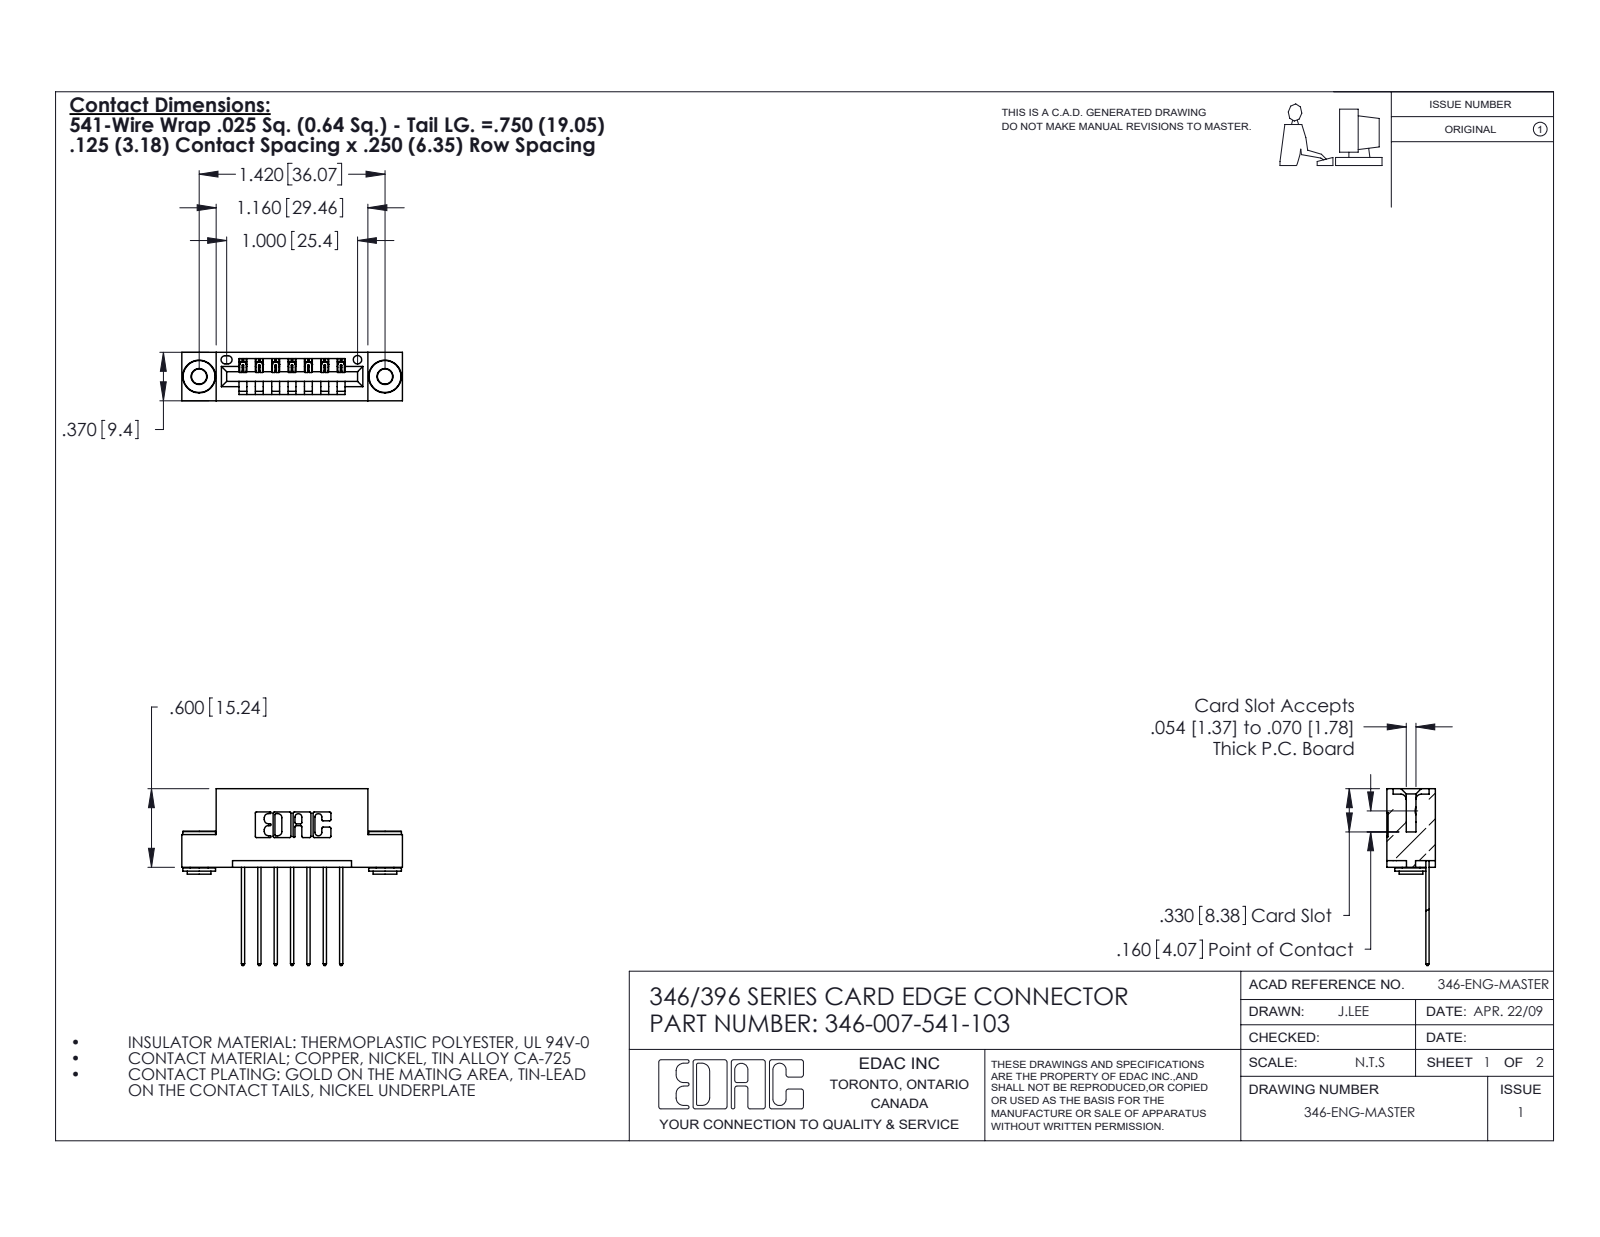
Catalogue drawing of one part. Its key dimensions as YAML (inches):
part_name: "345-292-001_345-293-141; 345-250-002_345-250-002-102; 346-007-541-103; 346 Part_Flush Mounting Lugs - 0.156 Dia-TH"
step_written_by: "SolidWorks 2020 (CONFIG_CONTROL_DESIGN)"
units: inches
bodies: {solids: 10, faces: 580, planar: 380, cylindrical: 192, other: 8}
overall_size: [1.685, 1.35, 0.37]
volume: 0.237
surface_area: 7.535
round_holes:
  - {diameter: 0.116, count: 2}
  - {diameter: 0.156, count: 2}
  - {diameter: 0.064, count: 1}
round_bosses_or_shafts:
  - {diameter: 0.25, count: 2}
  - {diameter: 0.18, count: 2}
  - {diameter: 0.136, count: 2}
partial_cylinders:
  - {radius: 0.01, count: 22}
  - {radius: 0.006, count: 14}
  - {radius: 0.01, count: 14}
  - {radius: 0.007, count: 6}
  - {radius: 0.031, count: 6}
  - {radius: 0.026, count: 3}
  - {radius: 0.031, count: 2}
  - {radius: 0.04, count: 2}
face_to_face_distances: [0.25, 0.048, 0.322, 0.37, 0.025, 0.072, 0.298, 0.148, 0.222, 0.1]
hole_center_spacings: [0.246, 1.217, 1.42]
